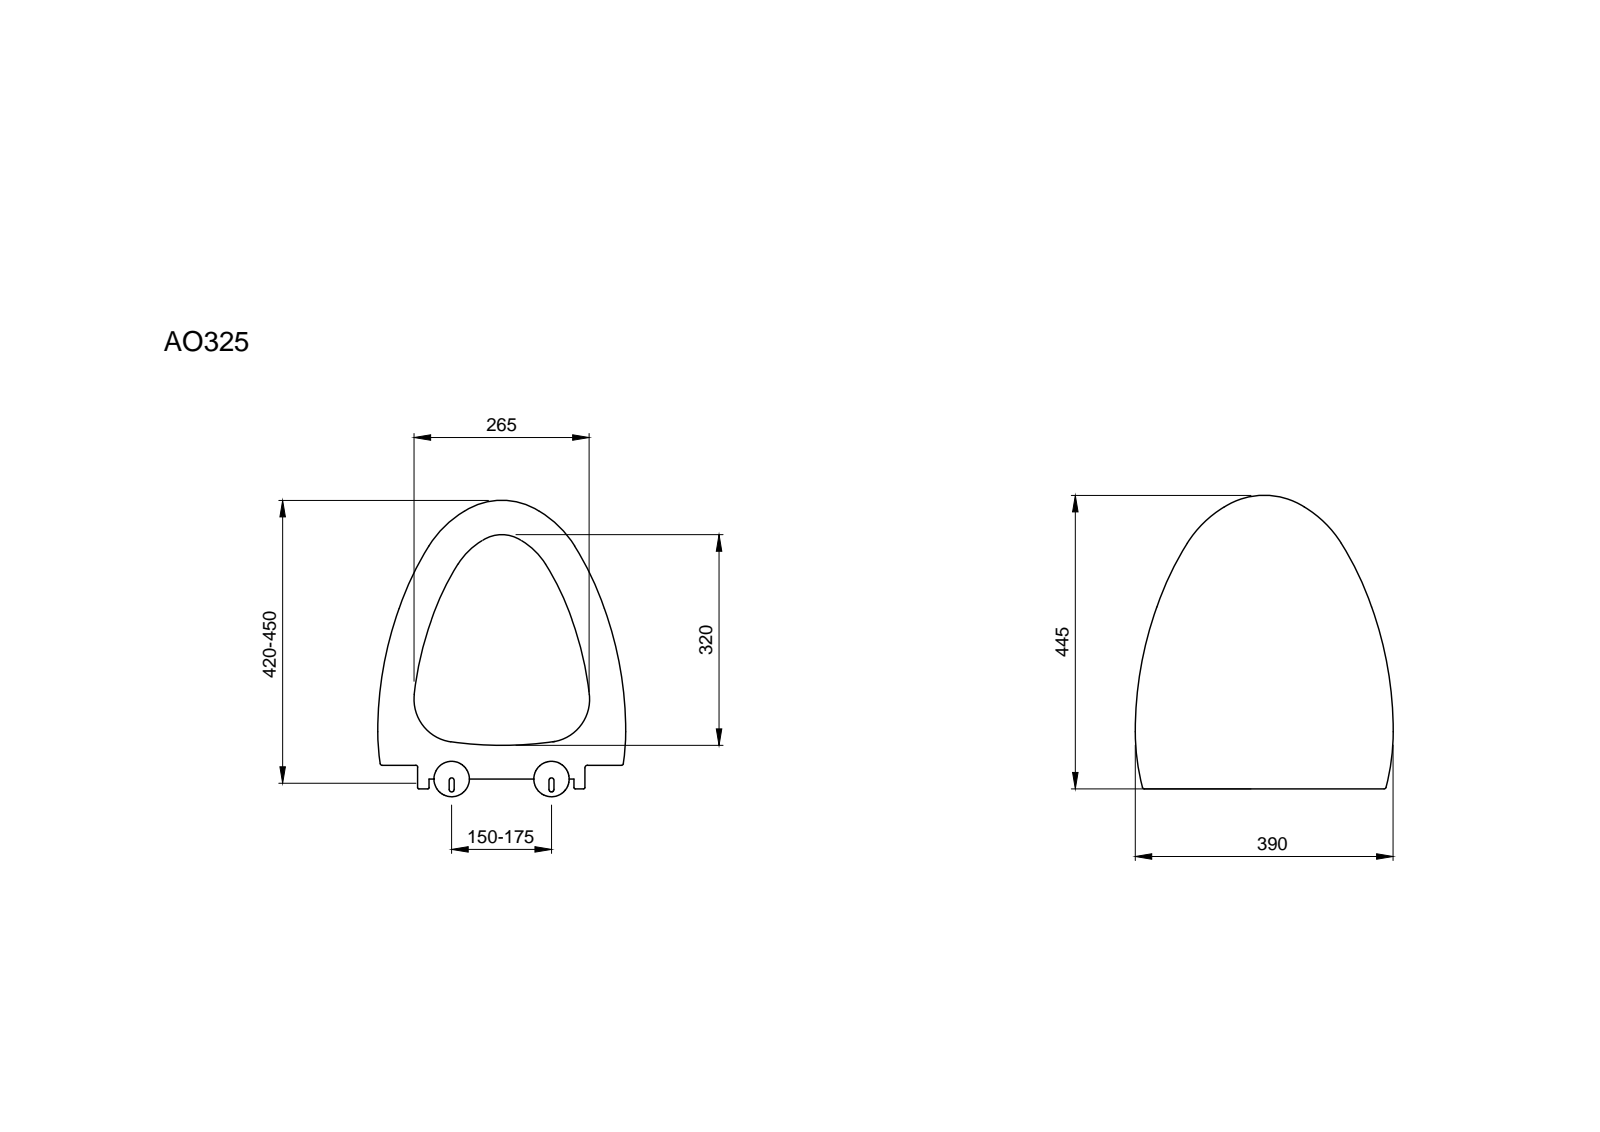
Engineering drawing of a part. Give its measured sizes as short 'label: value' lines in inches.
name: Can13403391kuli
written by: SIEMENS PLM Software NX 8.5 (AP203_CONFIGURATION_CONTROLLED_3D_DESIGN_OF_MECHANICAL_PARTS_AND_ASSEMBLIES_MIM_LF)
unit: in
bodies: 4 solids, 449 faces (35 planar, 30 cylindrical, 384 other)
size: 19.803 × 17.667 × 15.457
volume: 96.54 in³; area: 921.8 in²
holes: 2× ⌀0.315
bosses: 2× ⌀0.472, 1× ⌀0.945
rounds: 8× R0.433, 4× R0.039, 2× R0.079, 2× R0.118, 1× R0.591
face distances: 0.197, 0.157, 0.039, 1.496, 7.145, 0.669, 2.165, 7.814, 9.31, 8.641
hole spacings: 7.46
